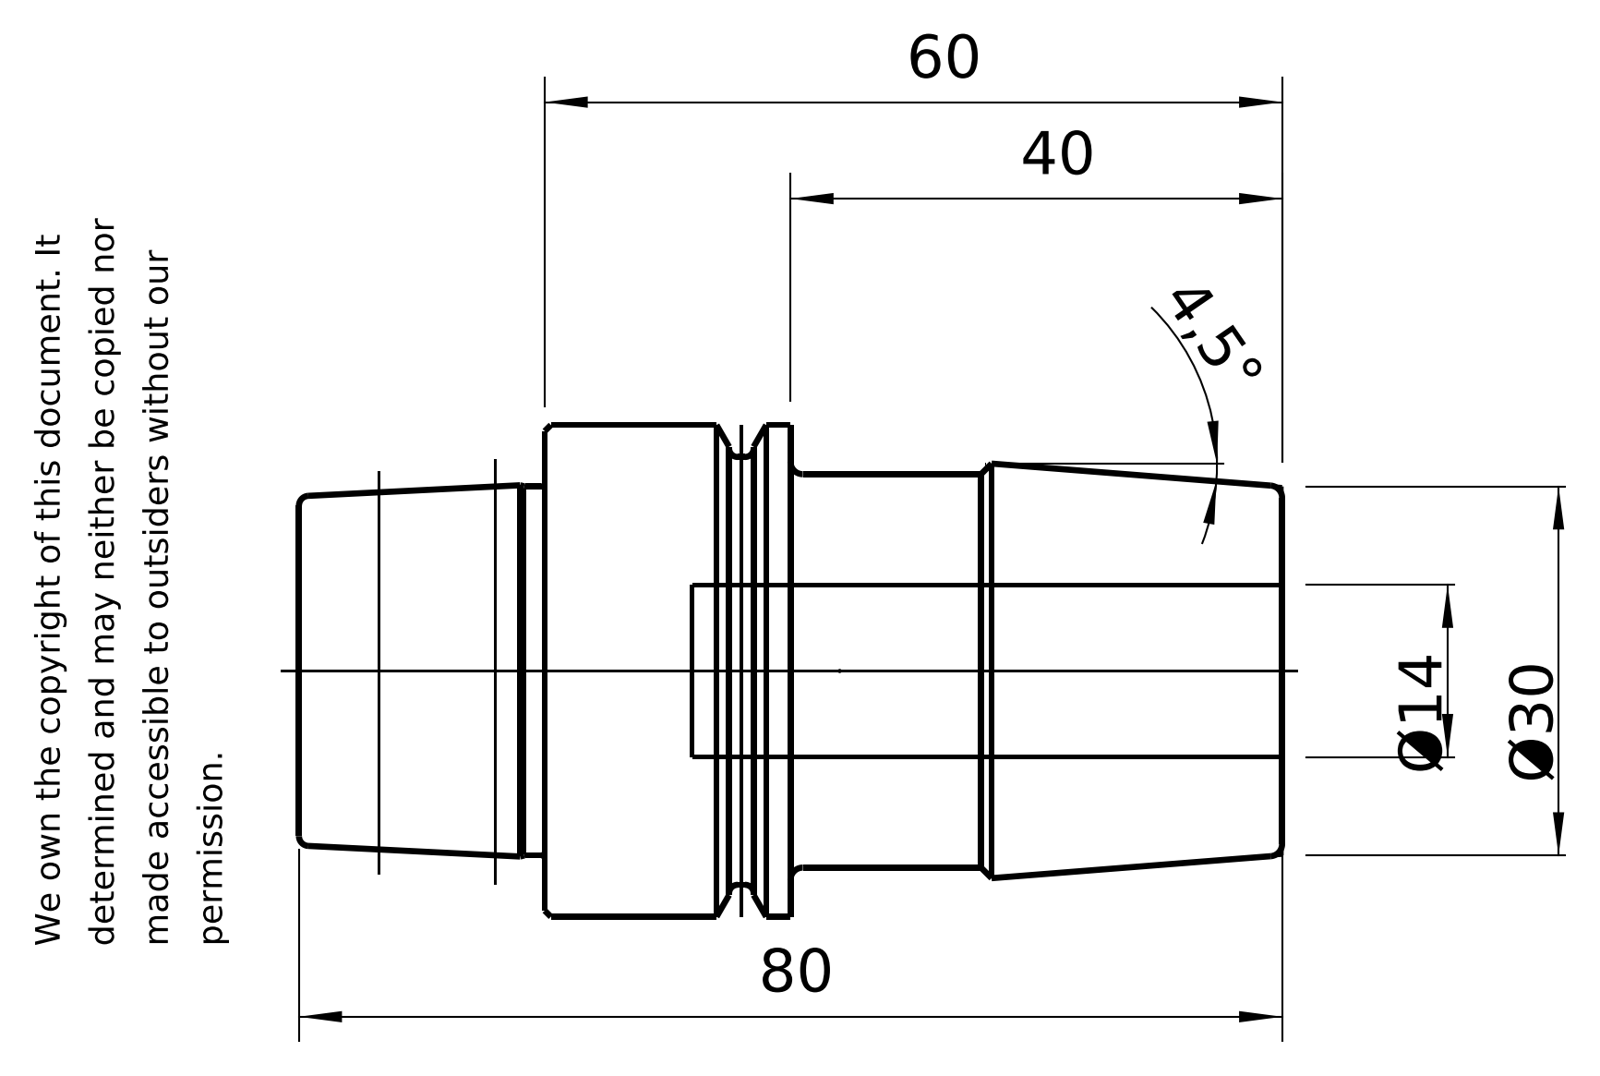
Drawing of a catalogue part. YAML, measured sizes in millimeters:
part_name: "E40-145-14"
step_written_by: "PRO/ENGINEER BY PARAMETRIC TECHNOLOGY CORPORATION, 2010430 (CONFIG_CONTROL_DESIGN)"
units: millimeters
bodies: {solids: 1, faces: 67, planar: 9, cylindrical: 18, other: 40}
overall_size: [79.9, 40, 40]
volume: 50972
surface_area: 15283
round_holes:
  - {diameter: 14, count: 1}
  - {diameter: 21.04, count: 1}
  - {diameter: 25.57, count: 1}
round_bosses_or_shafts:
  - {diameter: 40, count: 1}
  - {diameter: 34.75, count: 1}
  - {diameter: 32, count: 1}
  - {diameter: 29.81, count: 1}
face_to_face_distances: [7.95, 12, 60, 19.95, 40.05, 52.05, 19.9, 27.85, 39.85, 79.9]
